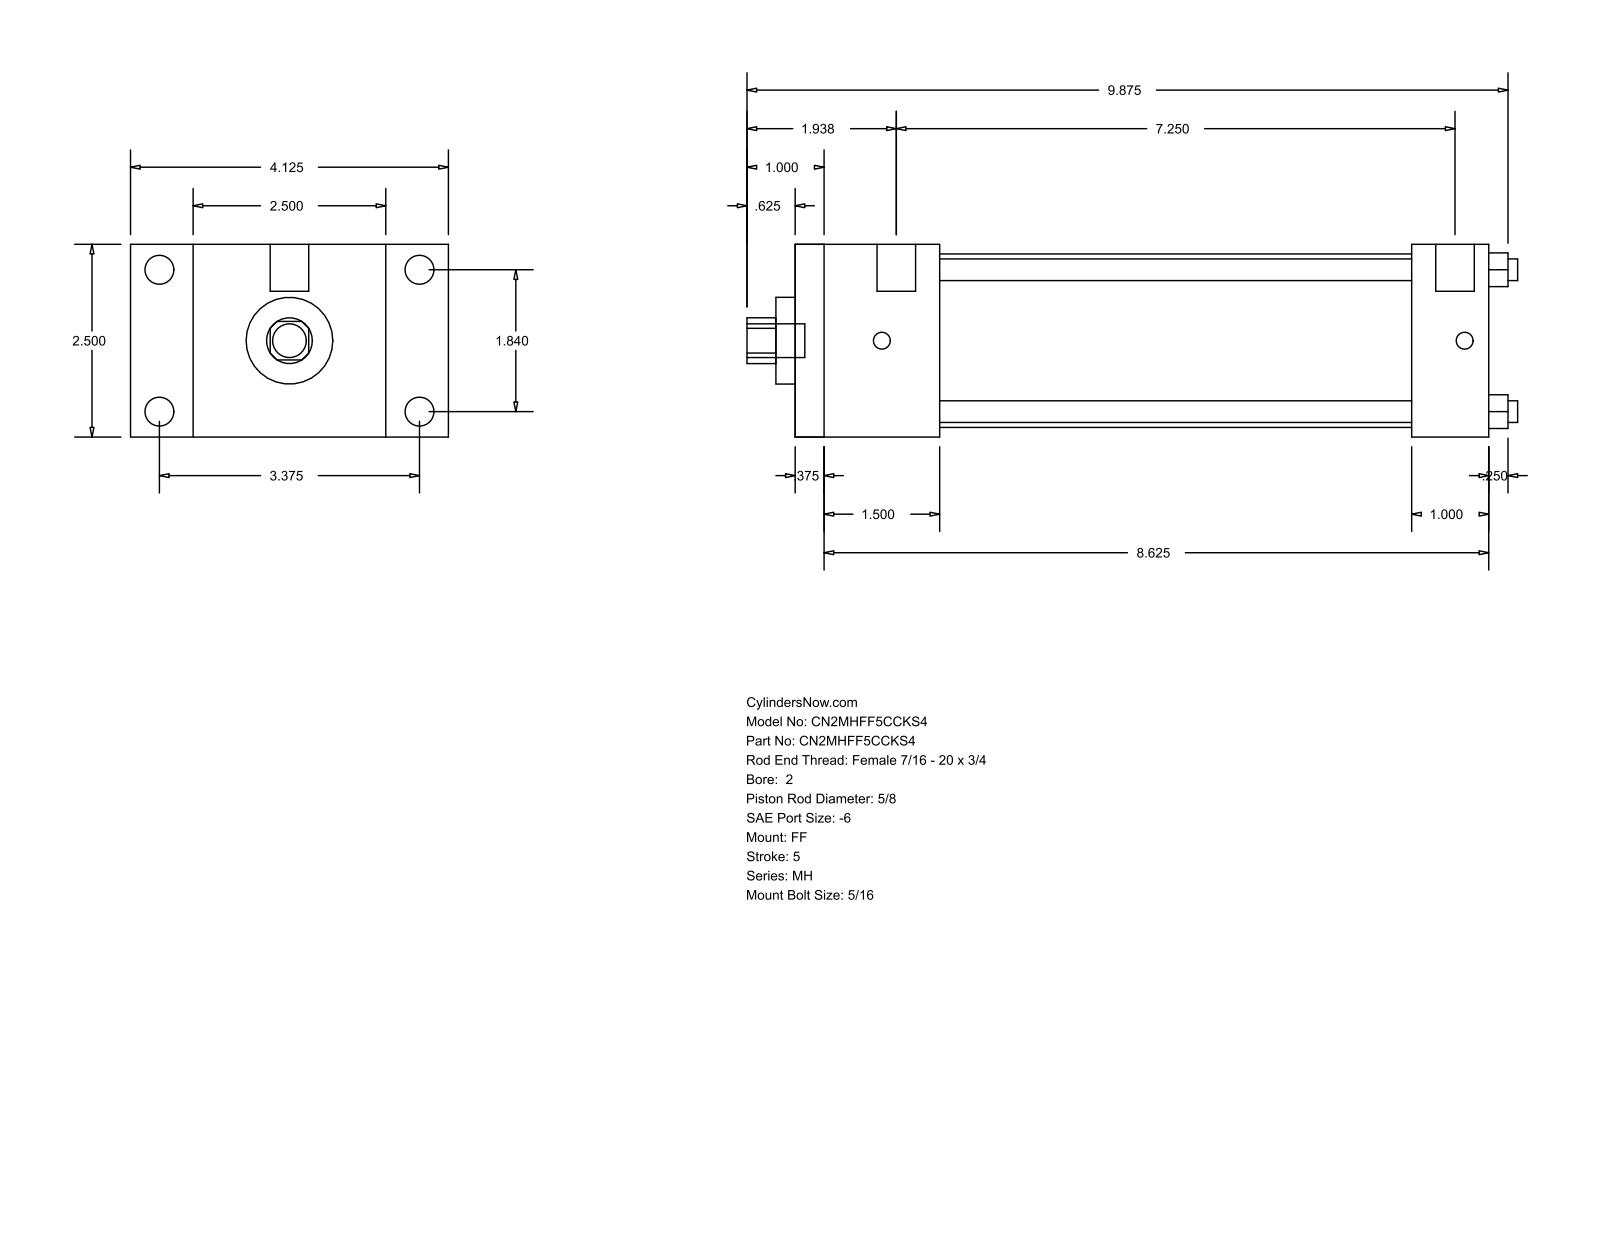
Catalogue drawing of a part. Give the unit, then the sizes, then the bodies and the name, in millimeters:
Units: millimetres
Overall size (bounding box): 254 × 104.78 × 63.5
Round holes (diameter × count): ⌀7.14 ×4, ⌀15.88 ×1, ⌀28.57 ×1, ⌀57.15 ×1
Round bosses / shafts (diameter × count): ⌀9.53 ×4, ⌀5.56 ×4, ⌀12.7 ×2, ⌀11.11 ×1
Partial cylindrical surfaces — rounded edges, fillets, slot ends (radius × count): R7.54 ×1
Main face-to-face distances: 63.5, 228.59, 9.52, 219.07, 25.4, 38.1, 47.62, 203.19, 193.67, 155.57
Hole centre spacings: 33.05, 46.74, 66.1
Bodies: 0 solids, 92 faces (64 planar, 28 cylindrical, 0 other)
Part name (STEP PRODUCT): MH_FF__0200_0.625
STEP written by: GSSL Pune (CONFIG_CONTROL_DESIGN)
